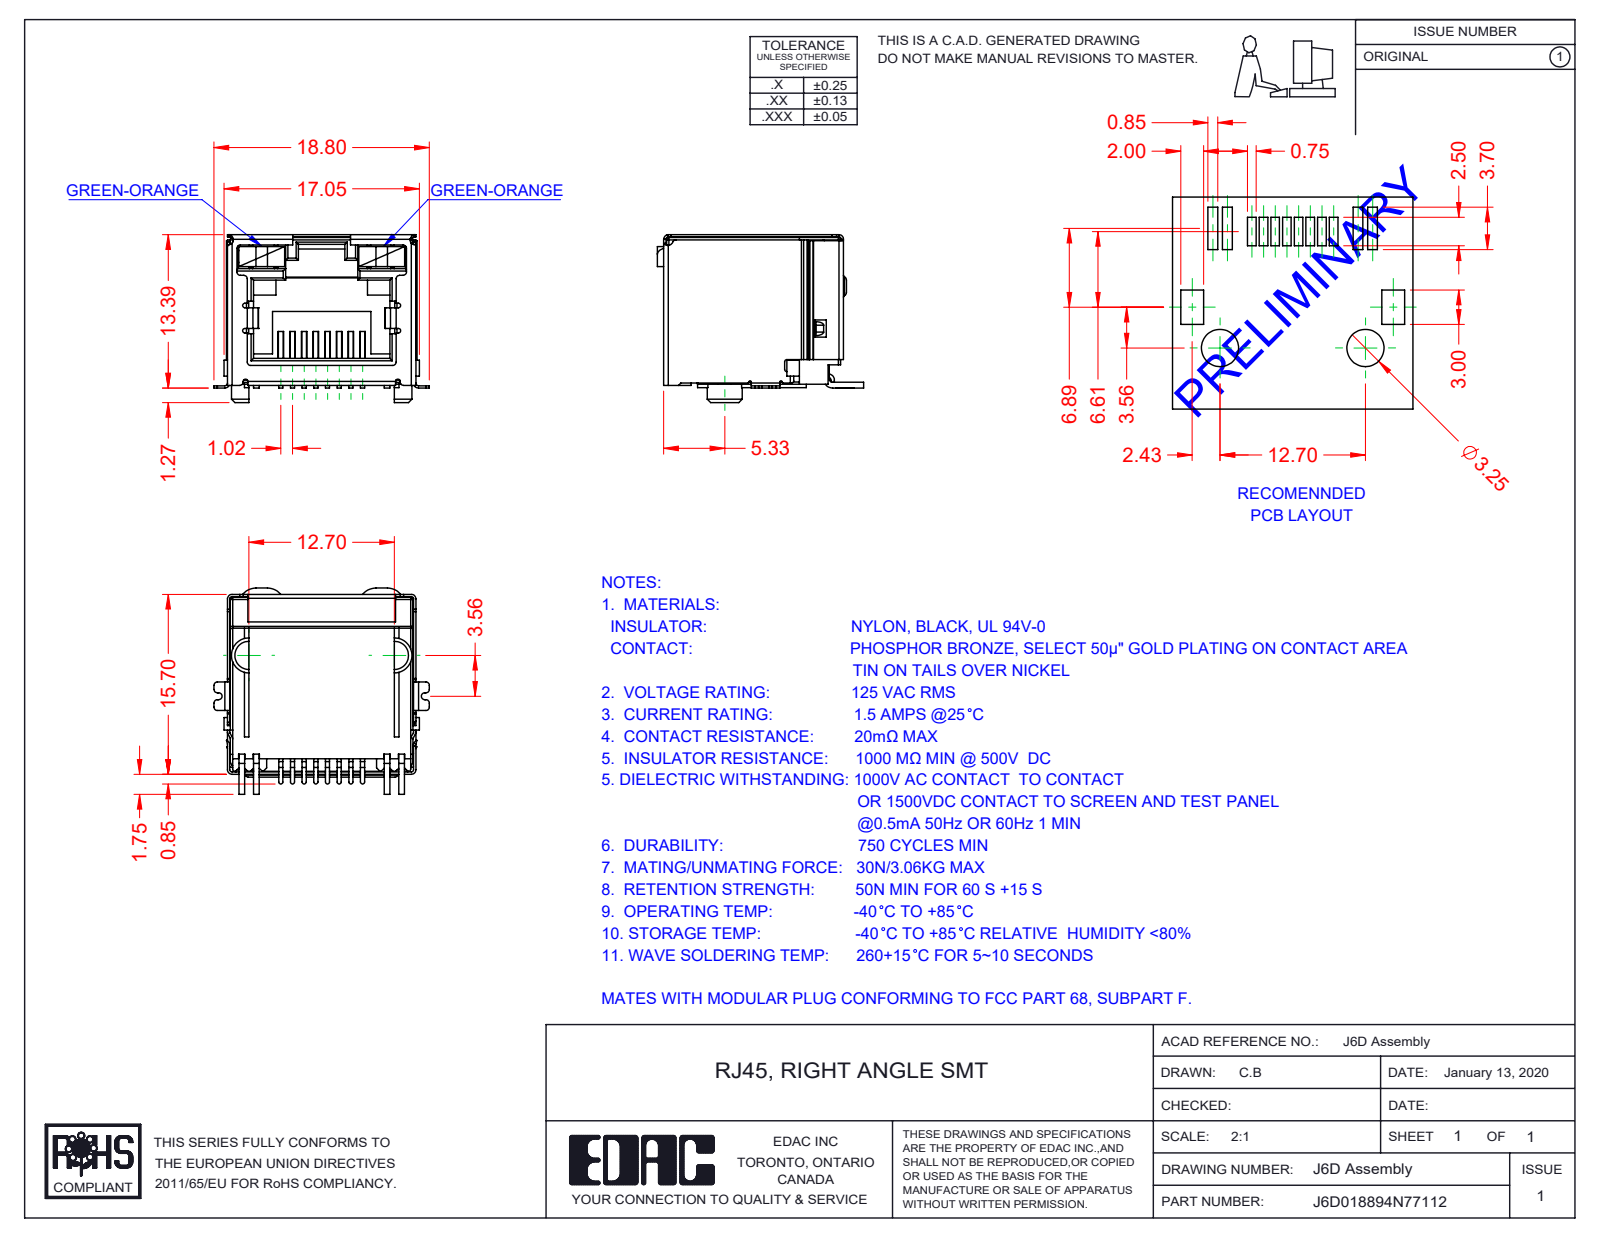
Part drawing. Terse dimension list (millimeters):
name: 6D Shield_LED - No EMI; 6D LED LH_7-Green-Orange; J6D018894N77112; 6D LED RH_7-Green-Orange (+2 more)
written by: SolidWorks 2016 (CONFIG_CONTROL_DESIGN)
unit: mm
bodies: 12 solids, 899 faces (646 planar, 220 cylindrical, 33 other)
size: 18.8 × 18 × 14.65
volume: 1 804 mm³; area: 4 898 mm²
rounds: 39× R0.3, 37× R0.2, 16× R0.4, 12× R0.1, 8× R0.15, 8× R0.18, 6× R0.5, 5× R1.5
face distances: 16, 16.25, 16.2, 2.25, 1, 15.95, 16.05, 12.8, 0.45, 16.45
